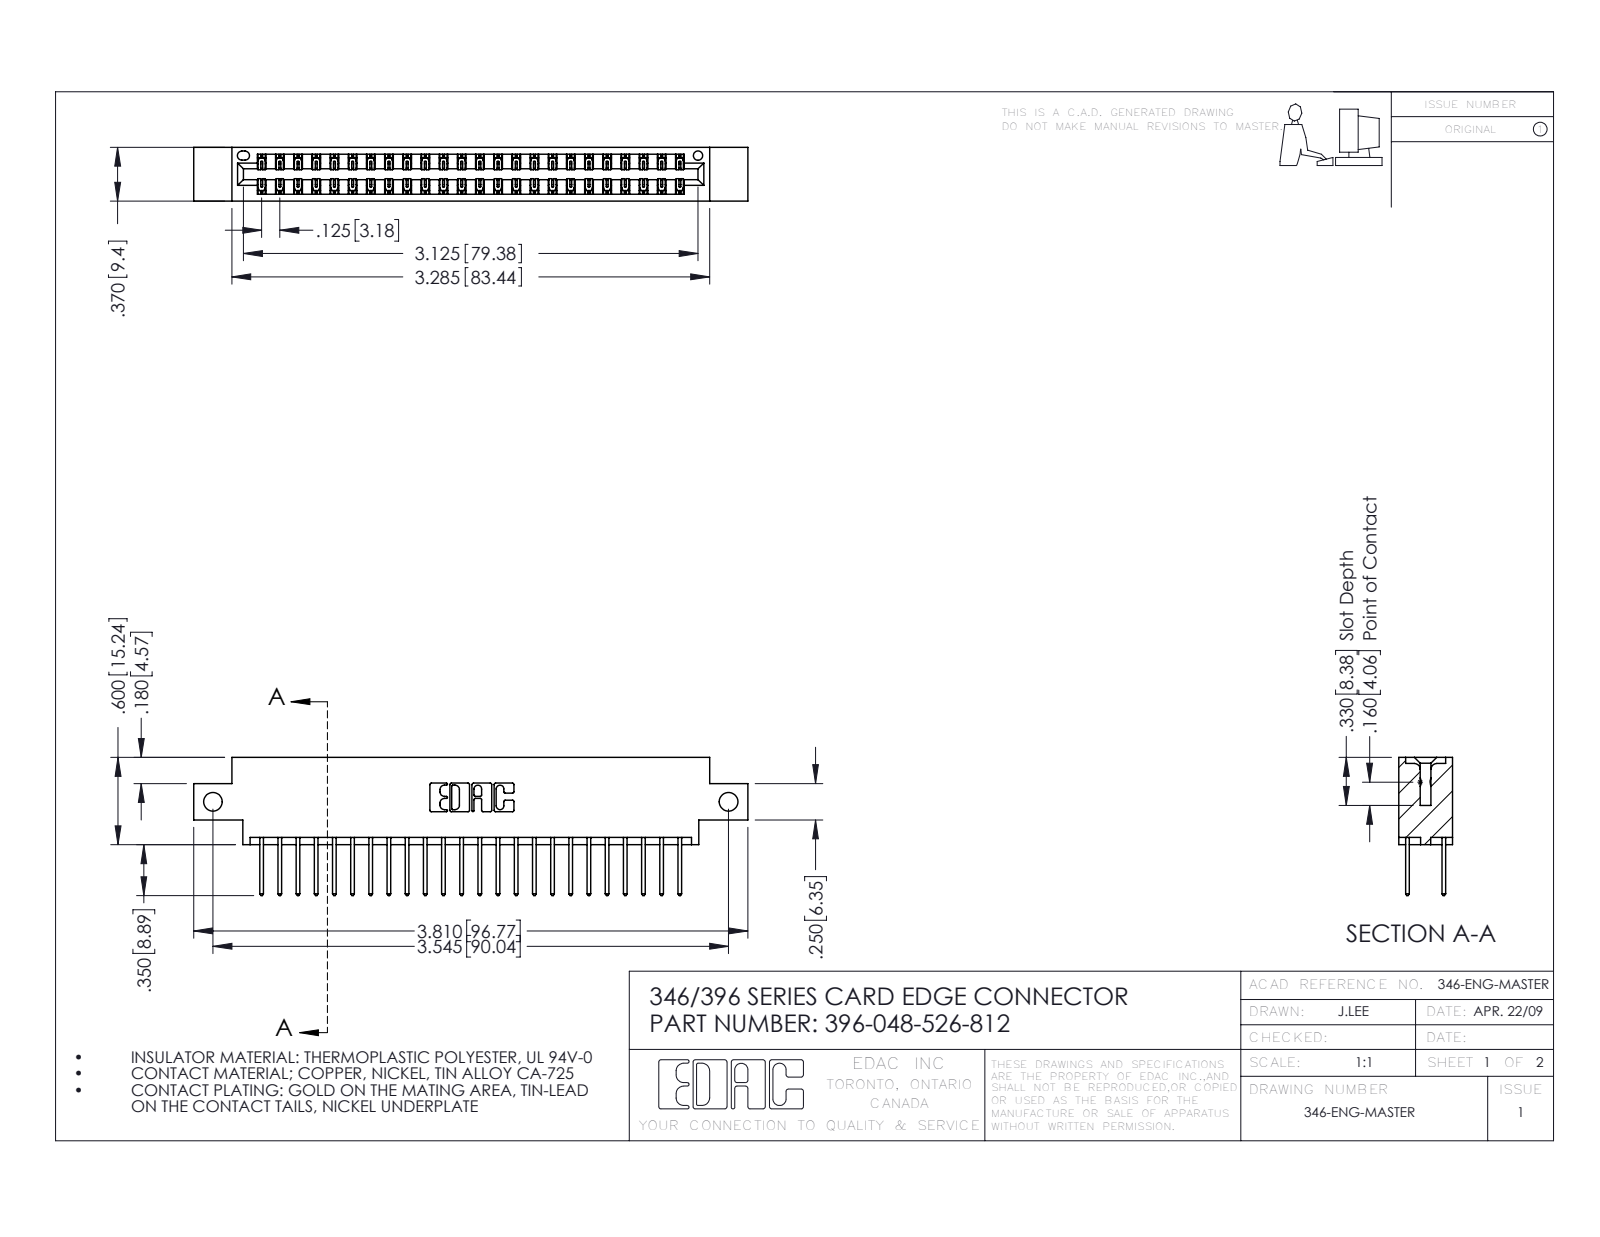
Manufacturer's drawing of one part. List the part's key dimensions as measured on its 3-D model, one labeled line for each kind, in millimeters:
Part name (STEP PRODUCT): 345-292-001_345-293-126; 346 Part_0.170 Offset - Side Mount; 396-048-526-812
STEP written by: SolidWorks 2016 (CONFIG_CONTROL_DESIGN)
Units: millimetres
Bodies: 49 solids, 2622 faces (1760 planar, 862 cylindrical, 0 other)
Overall size (bounding box): 96.8 × 24.1 × 9.4
Volume: 9 130 mm³ · Surface area: 12 660 mm²
Round holes (diameter × count): ⌀3.3 ×2, ⌀1.6 ×1
Partial cylindrical surfaces — rounded edges, fillets, slot ends (radius × count): R0.2 ×72, R0.3 ×48, R0.3 ×22, R0.2 ×6, R0.8 ×6, R0.7 ×3, R0.4 ×2, R0.6 ×2
Main face-to-face distances: 1.2, 8.2, 6.4, 9.4, 1.8, 7.6, 0.6, 7, 3.8, 5.6
Hole centre spacings: 90
